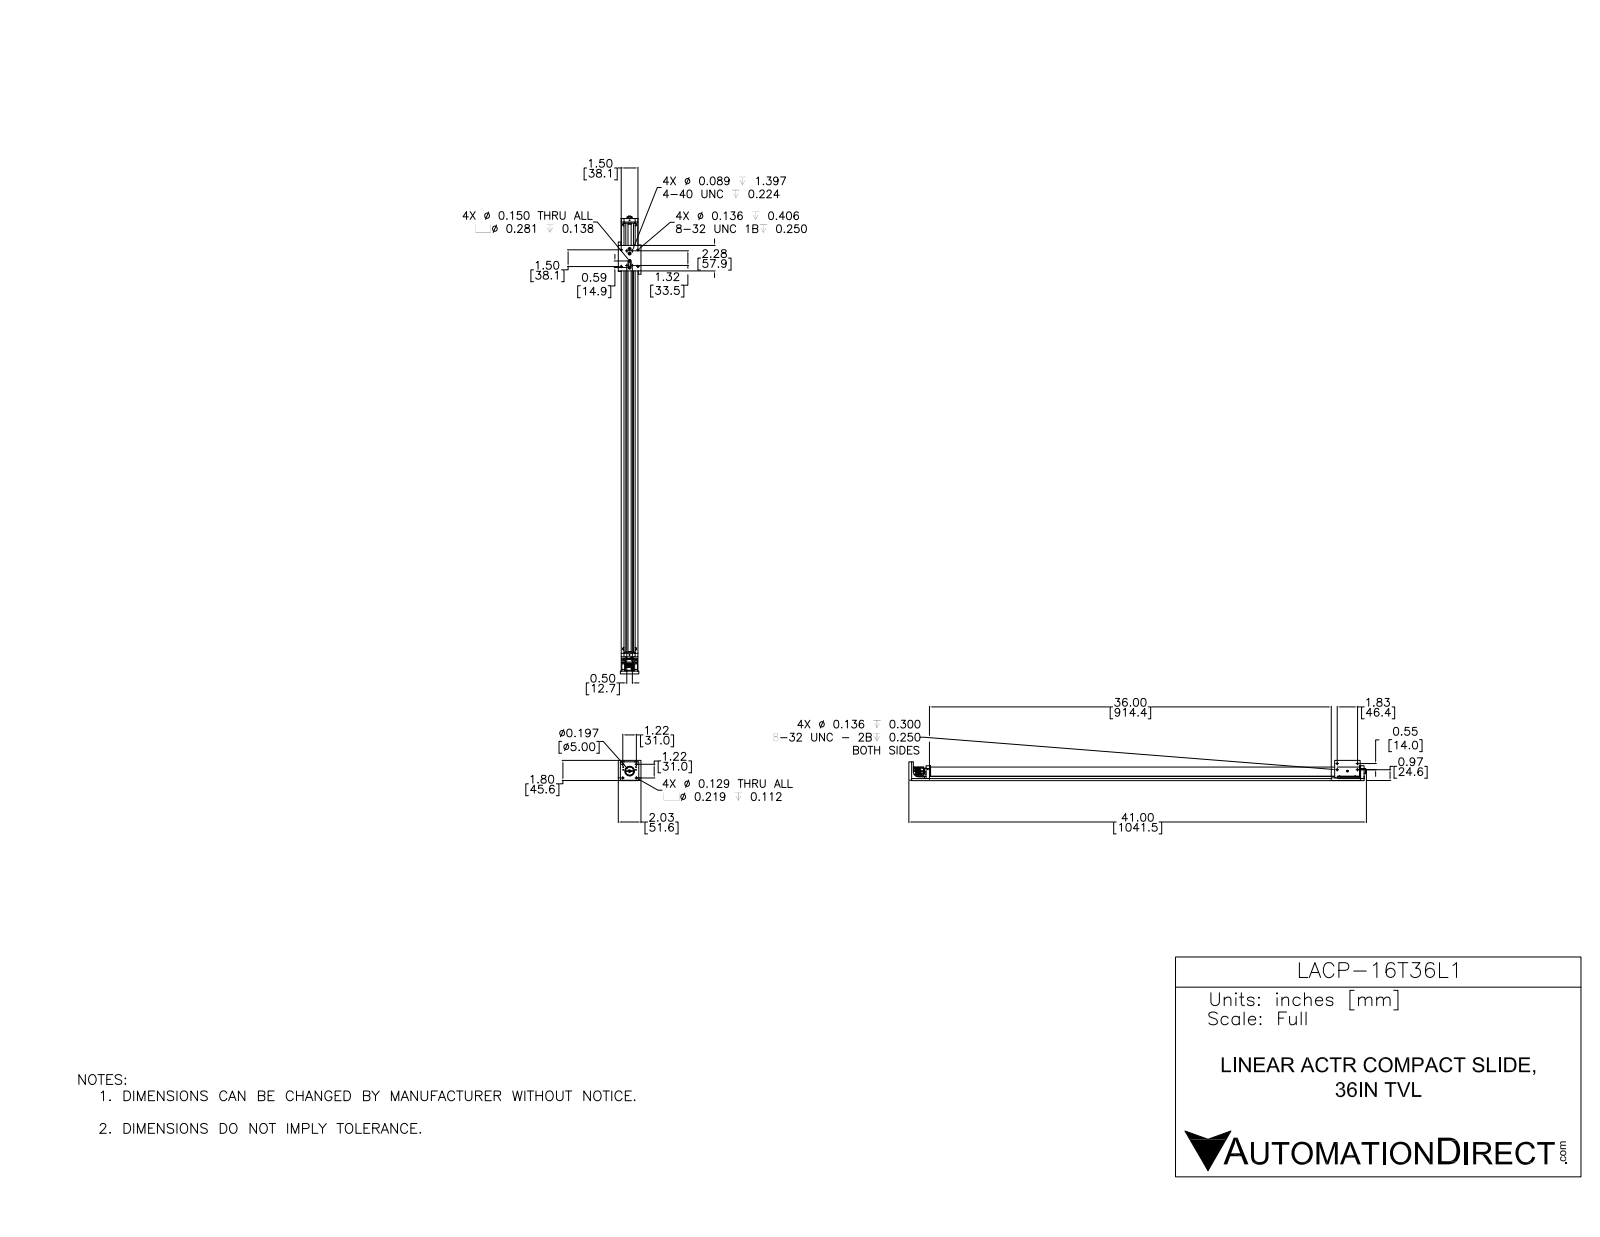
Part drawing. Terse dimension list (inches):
name: LACP-16T36L1; LACP-16TXXL1-CAR; LACP-16T36L1-RAIL
written by: SolidWorks 2016 (AUTOMOTIVE_DESIGN)
unit: in
bodies: 25 solids, 947 faces (289 planar, 562 cylindrical, 96 other)
size: 40.995 × 2.03 × 1.812
volume: 42.27 in³; area: 463.6 in²
holes: 22× ⌀0.281, 20× ⌀0.17, 16× ⌀0.089, 12× ⌀0.15, 10× ⌀0.138, 10× ⌀0.28, 8× ⌀0.136, 4× ⌀0.07, 4× ⌀0.129, 4× ⌀0.129, 4× ⌀0.219, 3× ⌀0.197
bosses: 3× ⌀0.157, 2× ⌀0.15, 1× ⌀1, 1× ⌀0.748, 1× ⌀0.71, 1× ⌀0.673, 1× ⌀0.67, 1× ⌀0.59
rounds: 4× R0.047, 4× R0.062, 4× R0.094, 3× R0.125, 2× R0.05, 2× R0.075, 2× R0.141, 2× R0.25
face distances: 0.187, 1.219, 1.031, 0.265, 1.765, 1.5, 0.875, 1.155, 0.61, 0.89
hole spacings: 4.031, 8, 4, 4.123, 8.016, 8.062, 12.01, 12
